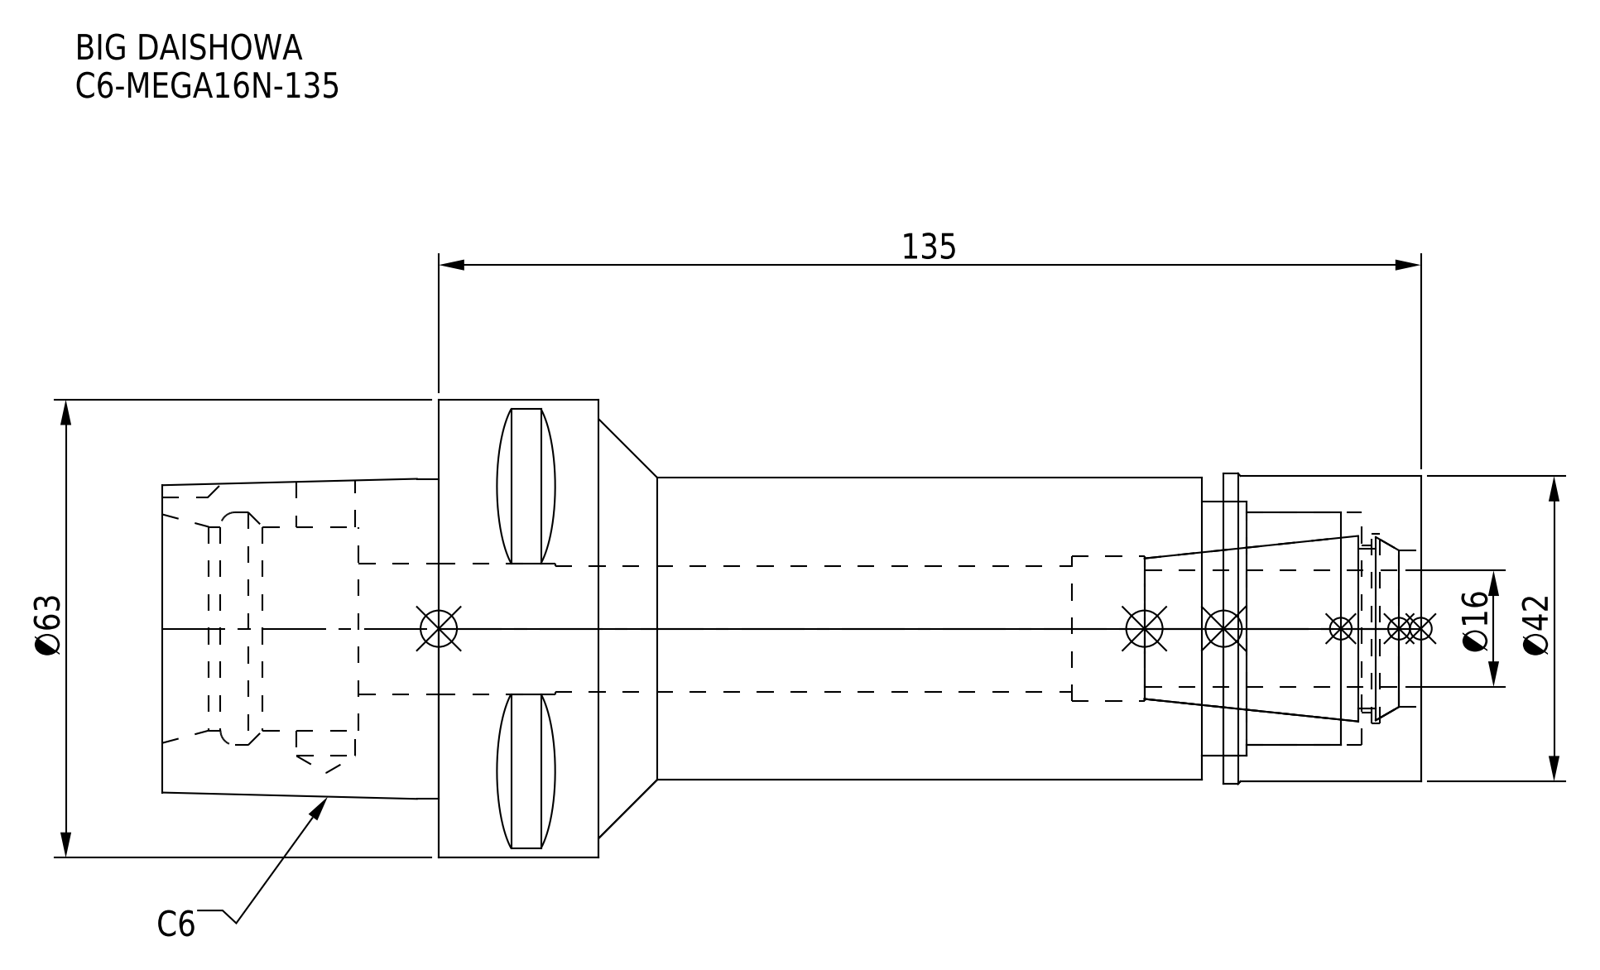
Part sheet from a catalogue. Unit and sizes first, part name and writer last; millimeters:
Units: millimetres
Overall size (bounding box): 173 × 63 × 63
Round holes (diameter × count): ⌀8.1 ×1, ⌀17.3 ×1, ⌀18 ×1, ⌀20 ×1, ⌀21.5 ×1, ⌀23 ×1, ⌀26 ×1, ⌀28 ×1, ⌀32 ×1, ⌀35 ×1
Round bosses / shafts (diameter × count): ⌀63 ×1, ⌀42.7 ×1, ⌀42 ×1, ⌀41.6 ×1
Partial cylindrical surfaces — rounded edges, fillets, slot ends (radius × count): R5 ×1
Main face-to-face distances: 135, 11, 38, 113, 22, 173, 60, 27.1, 85.9, 107.9
Volume: 218 565 mm³ · Surface area: 46 537 mm²
Bodies: 2 solids, 95 faces (38 planar, 39 cylindrical, 18 other)
Part name (STEP PRODUCT): DXF_TEMP_ASSY_ASM_4_ASM.stp; C6-MEGA16N-135_1.stp; C6-MEGA16N-135-160.stp; C6-MEGA16N-135 (+3 more)
STEP written by: SolidWorks 2019 (CONFIG_CONTROL_DESIGN)
